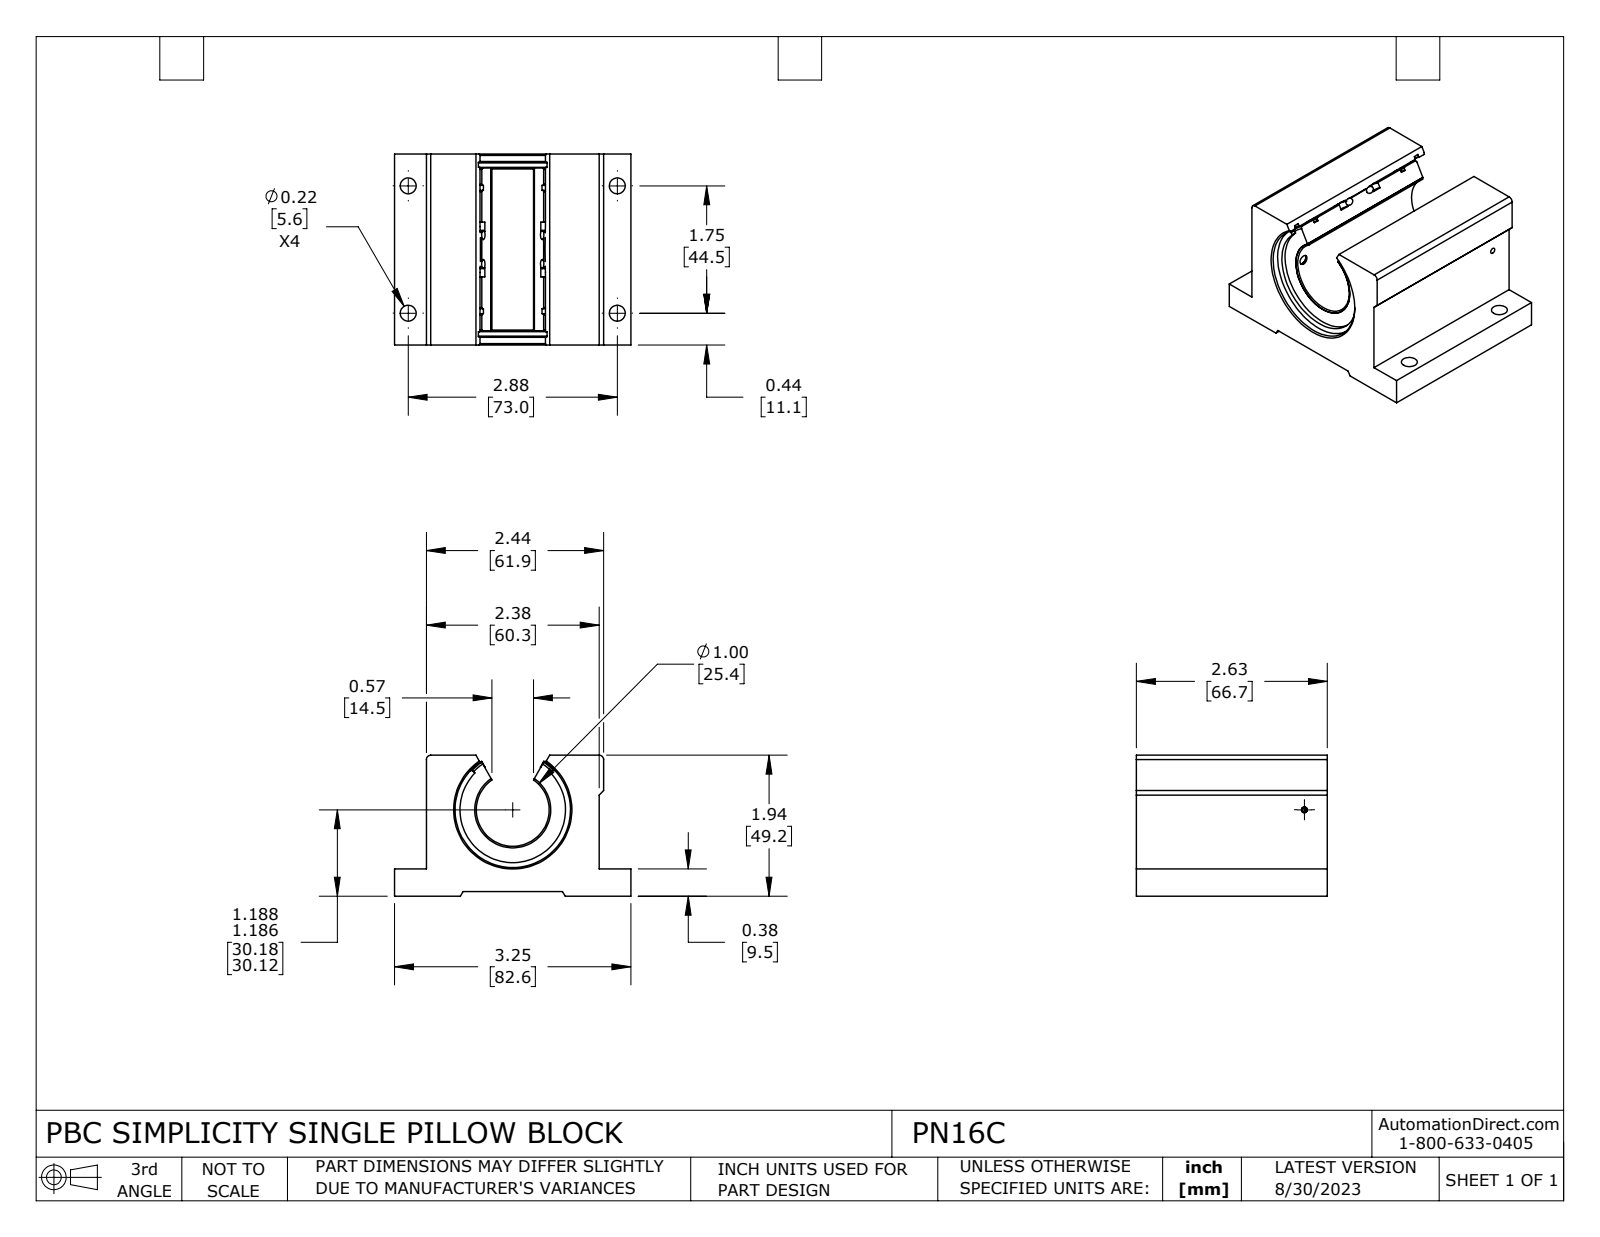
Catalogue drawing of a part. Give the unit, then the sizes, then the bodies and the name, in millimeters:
Units: millimetres
Overall size (bounding box): 82.6 × 66.7 × 49.2
Round holes (diameter × count): ⌀5.6 ×4, ⌀1.4 ×1, ⌀2 ×1, ⌀3.5 ×1, ⌀25.4 ×1, ⌀26.5 ×1, ⌀40.3 ×1, ⌀42.4 ×1
Round bosses / shafts (diameter × count): ⌀39.7 ×1, ⌀37.4 ×1, ⌀35.5 ×1, ⌀2 ×1
Partial cylindrical surfaces — rounded edges, fillets, slot ends (radius × count): R0.8 ×2, R1.5 ×2, R4.6 ×2, R18.4 ×1, R21.5 ×1
Main face-to-face distances: 1.7, 49.2, 47.6, 66.7, 60.3, 9.5, 7.9, 39.7, 11.1, 71.4
Hole centre spacings: 44.5, 73, 85.5, 50.6
Volume: 157 000 mm³ · Surface area: 51 540 mm²
Bodies: 8 solids, 206 faces (53 planar, 94 cylindrical, 59 other)
Part name (STEP PRODUCT): PN16C
STEP written by: SolidWorks 2021 (CONFIG_CONTROL_DESIGN)
